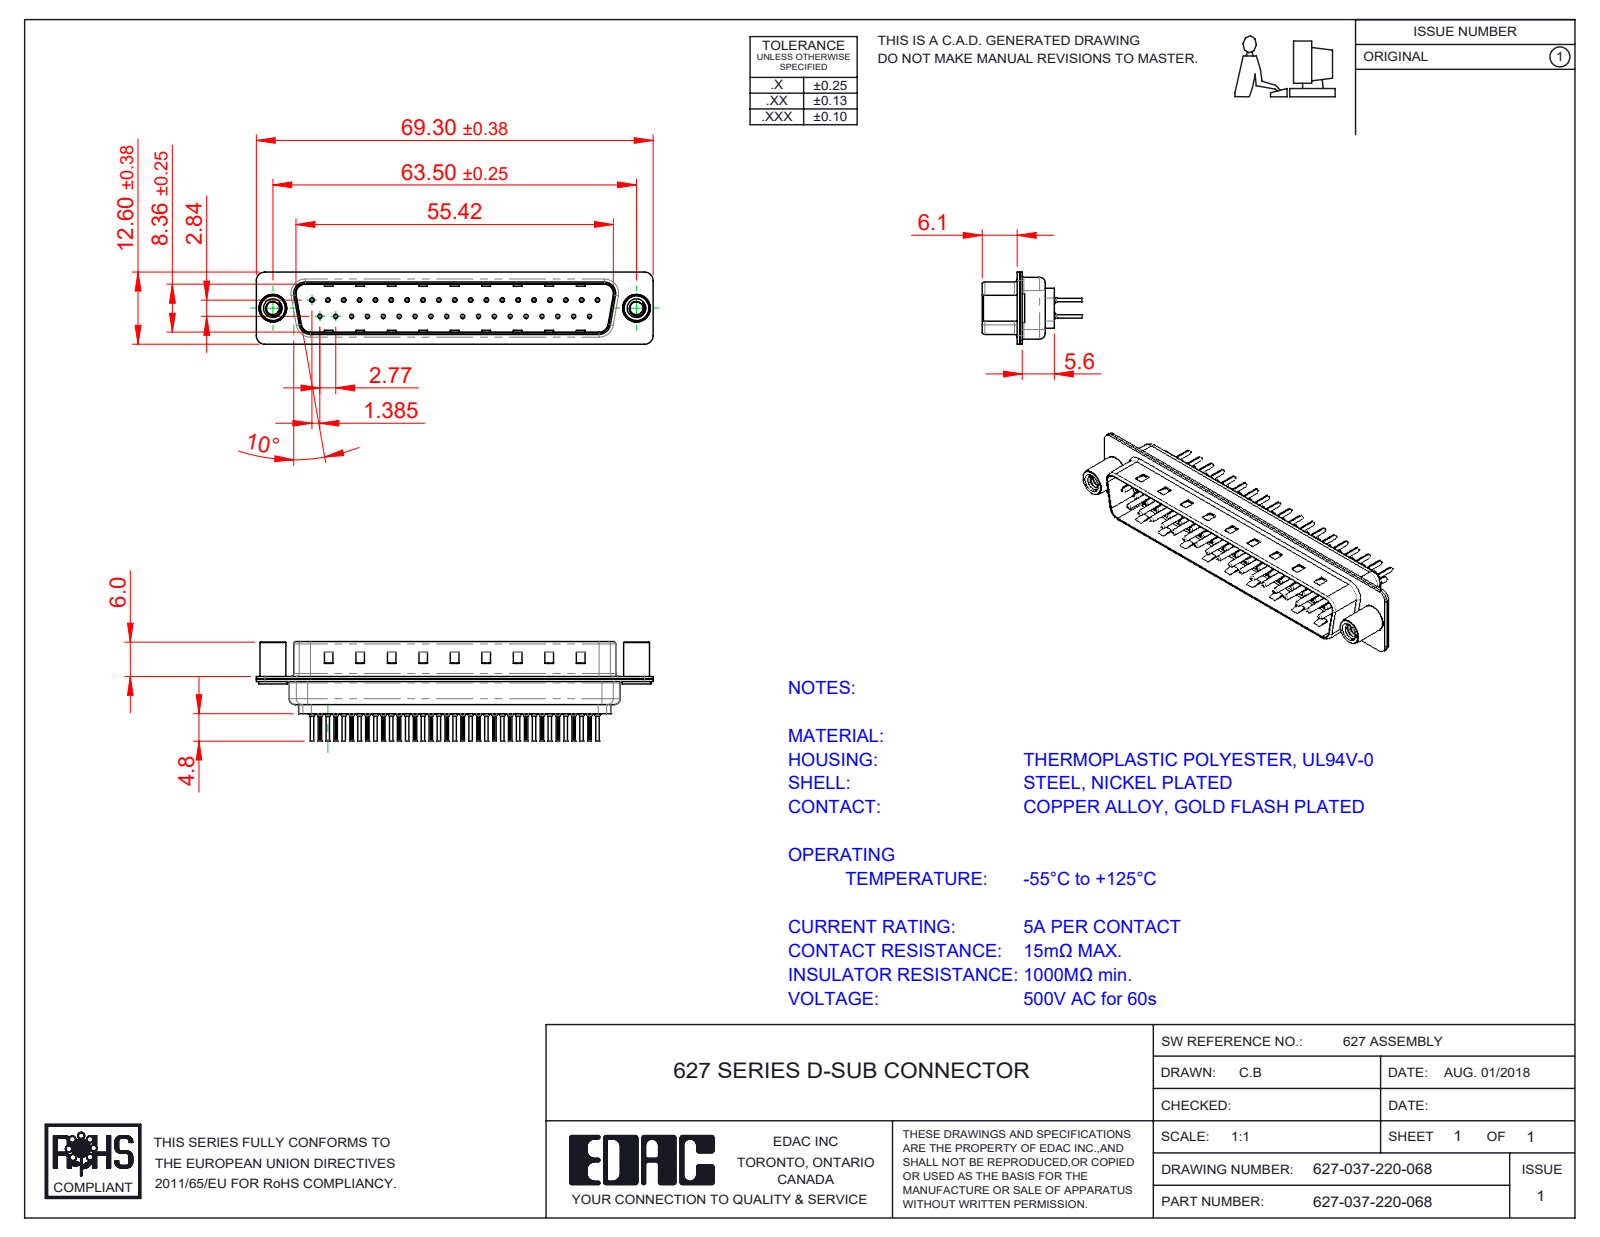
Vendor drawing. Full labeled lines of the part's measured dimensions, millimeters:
Part name (STEP PRODUCT): 627-037-220-068; 627 4-40 Threaded Standoff; 627 Contact Row 1_20L; 627 Contact Row 2_20L (+3 more)
STEP written by: SolidWorks 2020 (CONFIG_CONTROL_DESIGN)
Units: millimetres
Bodies: 42 solids, 4072 faces (1093 planar, 1538 cylindrical, 1441 other)
Overall size (bounding box): 69.3 × 17.3 × 12.6
Volume: 3 765 mm³ · Surface area: 10 875 mm²
Round holes (diameter × count): ⌀0.2 ×37, ⌀0.35 ×37, ⌀1.1 ×37, ⌀1.6 ×37, ⌀2.26 ×2, ⌀4 ×2, ⌀4.8 ×2
Round bosses / shafts (diameter × count): ⌀2 ×37, ⌀1.5 ×37, ⌀0.75 ×37, ⌀0.6 ×37, ⌀5 ×2, ⌀4.9 ×2, ⌀4.5 ×2
Partial cylindrical surfaces — rounded edges, fillets, slot ends (radius × count): R0.1 ×74, R1.5 ×16, R2 ×12, R0.5 ×8, R1.6 ×8, R0.25 ×4, R0.6 ×4, R0.65 ×4
Main face-to-face distances: 0.4, 0.82, 9.58, 0.45, 8.76, 1.5, 0.9, 1.4, 6.05, 0.42
Hole centre spacings: 3.16, 2.77, 5.54, 8.31, 5.04, 10.1, 11.08, 12.78
